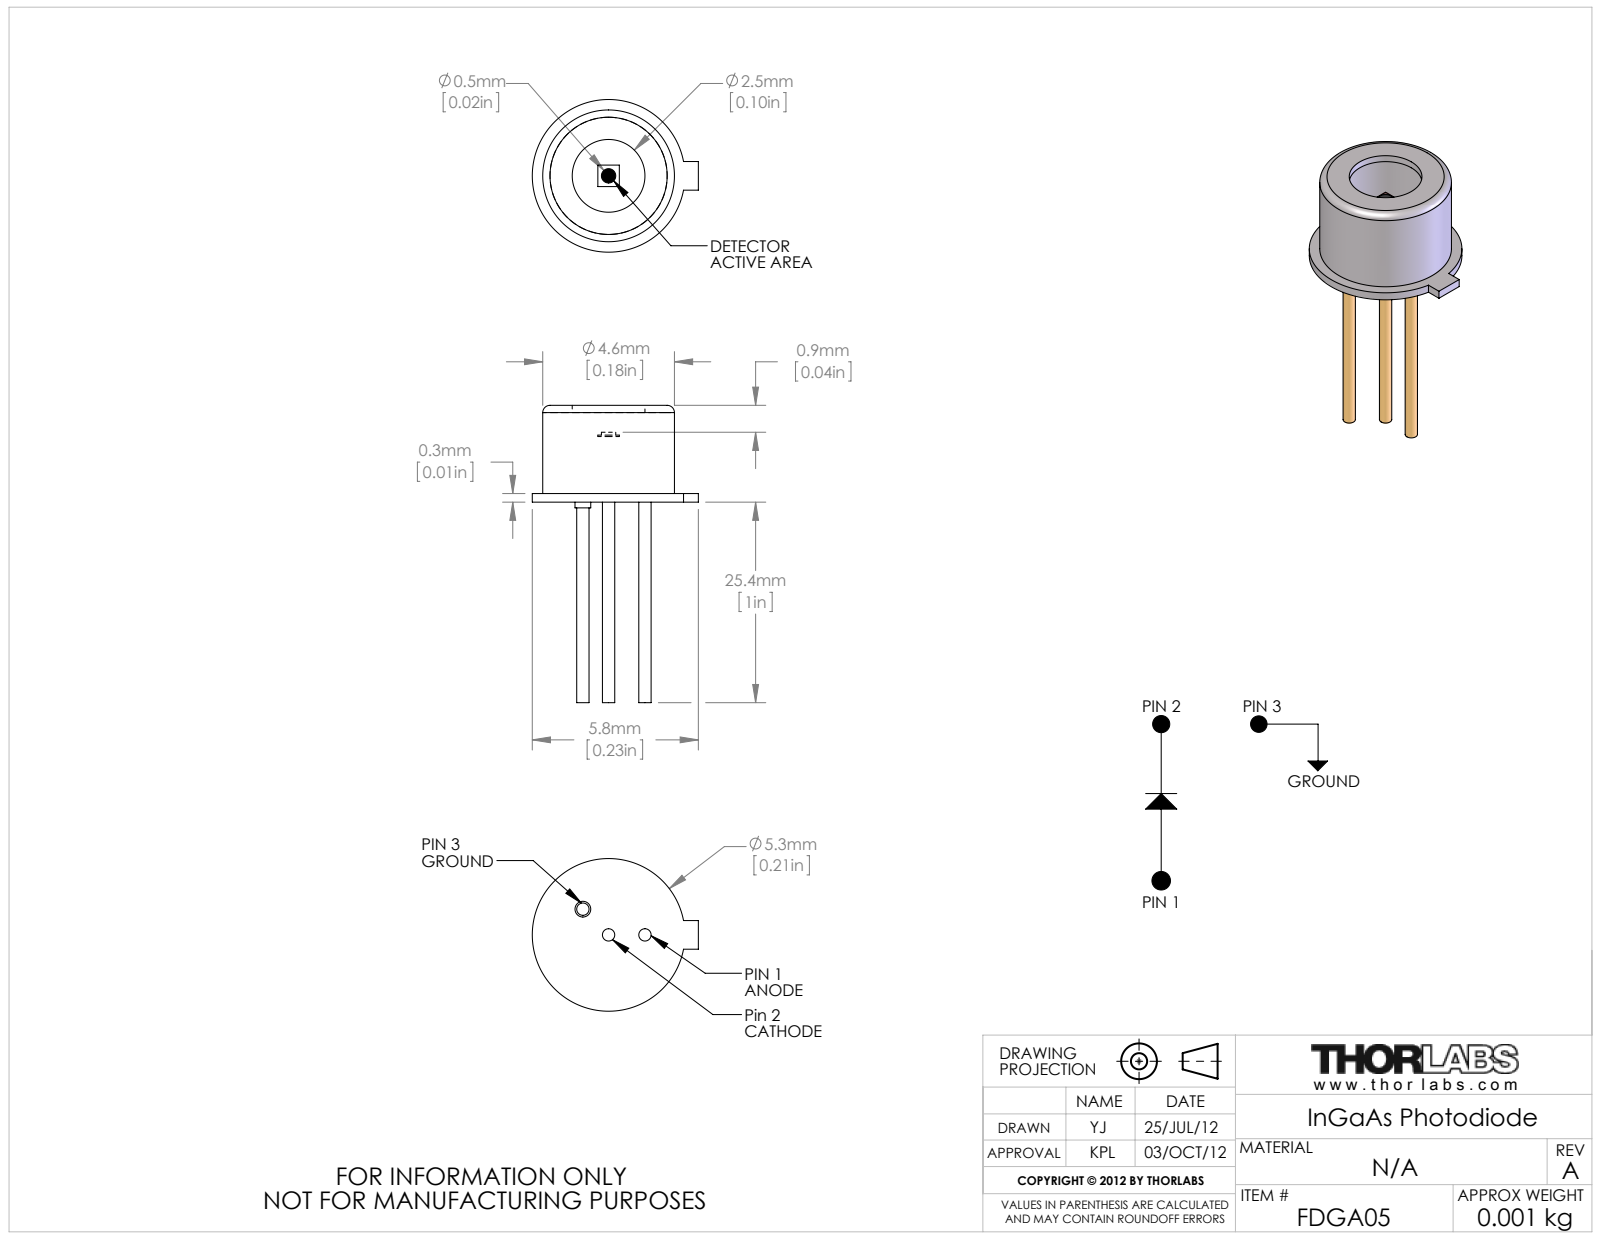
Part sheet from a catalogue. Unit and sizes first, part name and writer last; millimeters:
Units: millimetres
Overall size (bounding box): 10.38 × 5.8 × 5.33
Round holes (diameter × count): ⌀2.54 ×1, ⌀4.09 ×1
Round bosses / shafts (diameter × count): ⌀0.43 ×3, ⌀5.33 ×1, ⌀4.6 ×1, ⌀0.55 ×1, ⌀0.5 ×1
Main face-to-face distances: 3.08, 3.33, 3.13, 3.38, 2.83, 2.29, 2.24, 1.99, 0.84, 1.09
Volume: 19 mm³ · Surface area: 182 mm²
Bodies: 2 solids, 40 faces (19 planar, 19 cylindrical, 2 other)
Part name (STEP PRODUCT): 24705-E0W
STEP written by: SolidWorks 2011 (AUTOMOTIVE_DESIGN)
